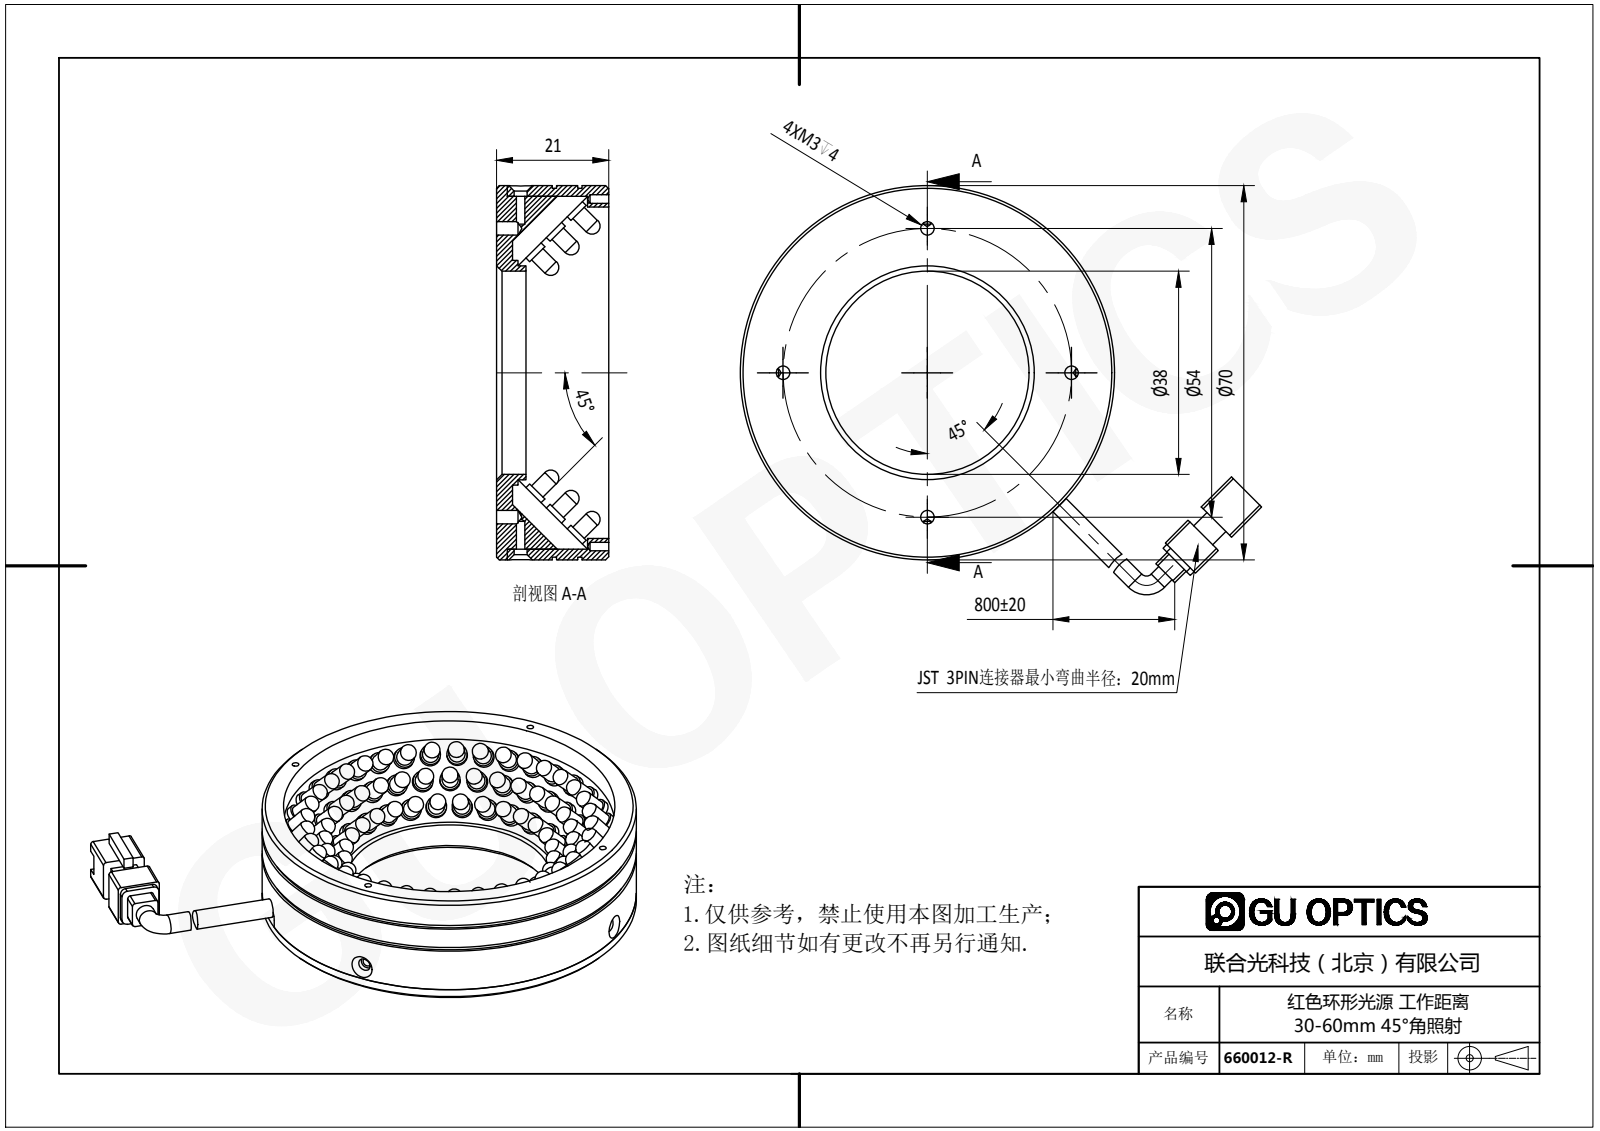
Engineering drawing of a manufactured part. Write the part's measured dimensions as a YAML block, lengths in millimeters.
part_name: "660012-R"
step_written_by: "SolidWorks 2016 (AUTOMOTIVE_DESIGN)"
units: millimeters
bodies: {solids: 103, faces: 1900, planar: 1251, cylindrical: 494, other: 155}
overall_size: [97.58, 76.52, 21]
volume: 29732
surface_area: 35149
round_holes:
  - {diameter: 1.25, count: 4}
  - {diameter: 2.5, count: 4}
  - {diameter: 3, count: 3}
  - {diameter: 1.6, count: 2}
  - {diameter: 2.4, count: 2}
  - {diameter: 38, count: 1}
  - {diameter: 62, count: 1}
round_bosses_or_shafts:
  - {diameter: 3.8, count: 98}
  - {diameter: 3, count: 97}
  - {diameter: 3.5, count: 2}
  - {diameter: 70, count: 1}
  - {diameter: 69, count: 1}
  - {diameter: 66, count: 1}
  - {diameter: 42, count: 1}
  - {diameter: 40, count: 1}
partial_cylinders:
  - {radius: 0.5, count: 8}
  - {radius: 1, count: 4}
  - {radius: 1.65, count: 1}
  - {radius: 5, count: 1}
face_to_face_distances: [1, 2, 3, 19, 4, 21, 17, 18, 0.5, 14]
hole_center_spacings: [42.25, 5.5, 27, 32.5, 38.18, 45.96, 59.5, 54]
